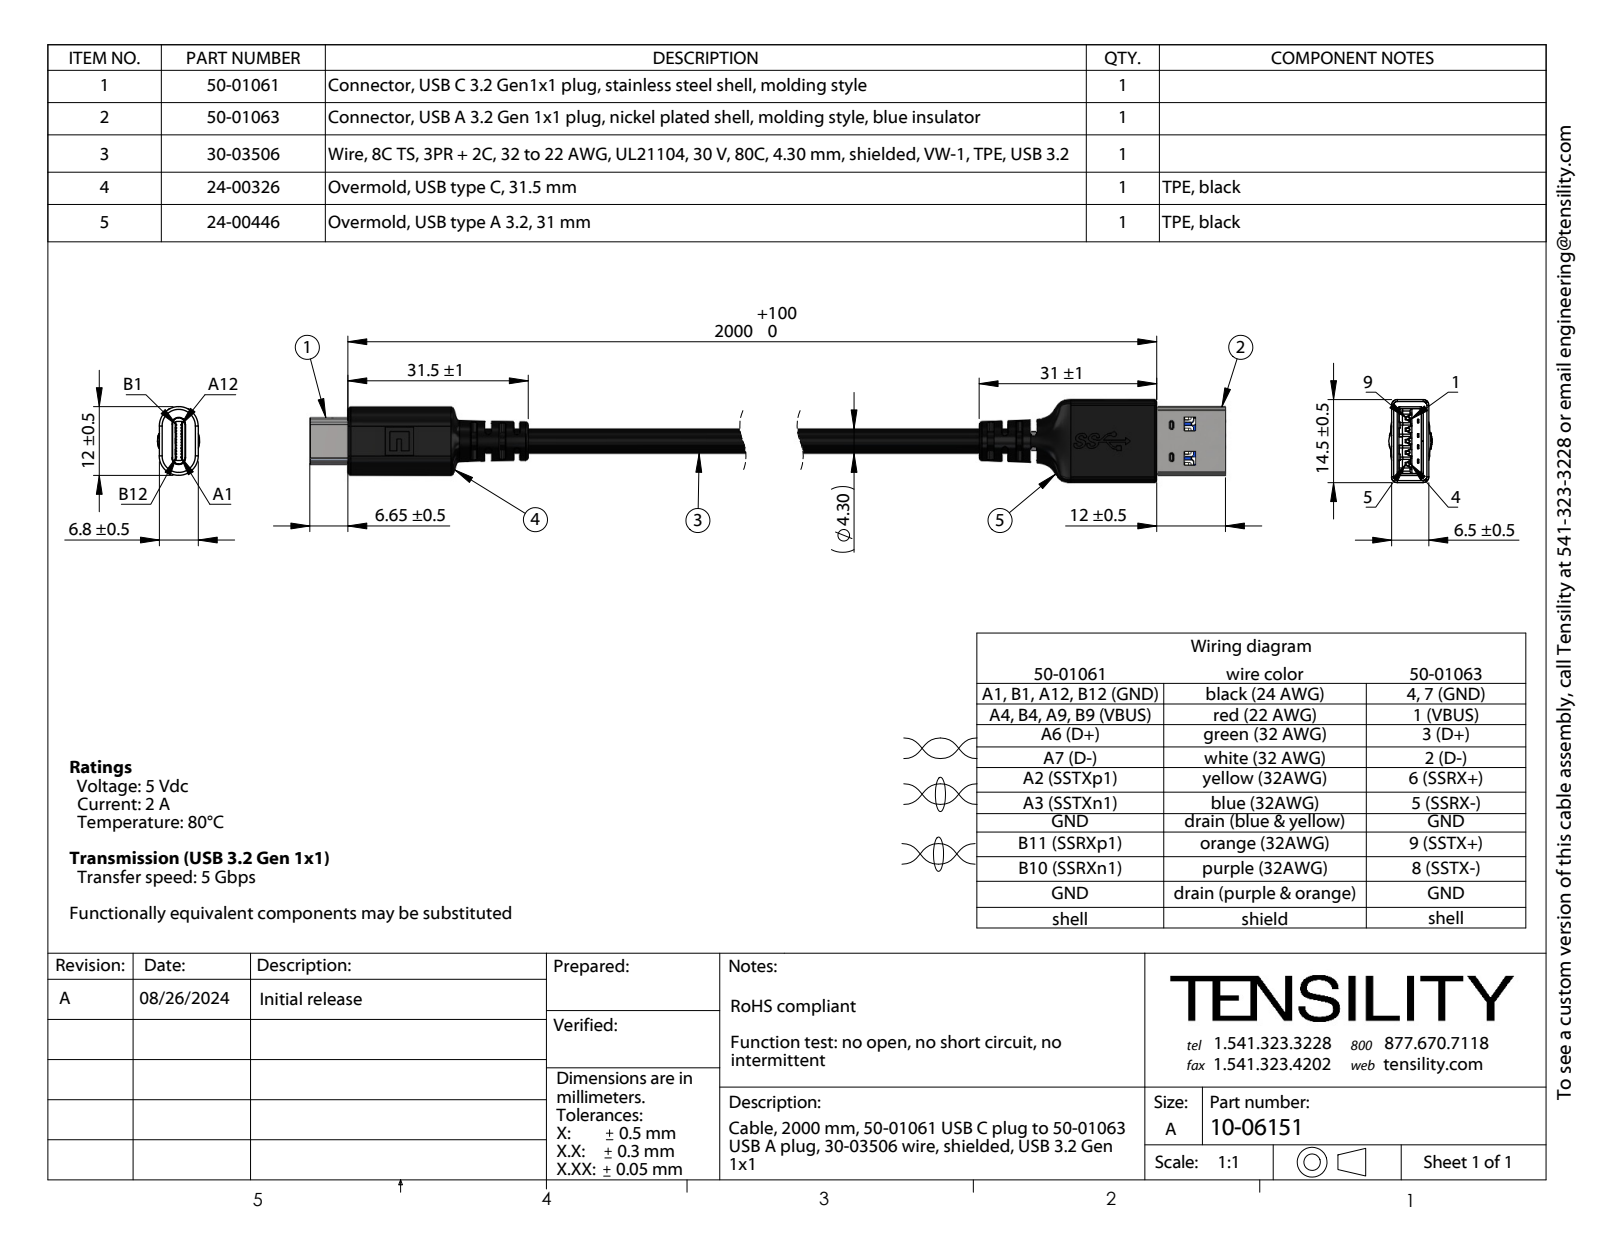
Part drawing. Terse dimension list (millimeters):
name: 50-01063_pin4; 30-03506_Spec; 50-01063_insulator; 50-01063_shell (+8 more)
written by: SolidWorks 2021 (CONFIG_CONTROL_DESIGN)
unit: mm
bodies: 184 solids, 2646 faces (1399 planar, 829 cylindrical, 418 other)
size: 211.15 × 14.5 × 7.54
volume: 5 792 mm³; area: 26 919 mm²
holes: 1× ⌀0.87, 1× ⌀3.23, 1× ⌀3.35
bosses: 4× ⌀0.6, 2× ⌀0.75, 2× ⌀0.55, 2× ⌀0.45, 1× ⌀4.3, 1× ⌀3.25, 1× ⌀1.66, 1× ⌀1
rounds: 30× R0.1, 24× R0.2, 20× R0.5, 13× R0.3, 10× R0.4, 9× R0.25, 7× R0.35, 7× R0.6
face distances: 0.89, 4.25, 0.9, 2.5, 0.35, 6.5, 0.88, 3.1, 1.28, 0.98
hole spacings: 0.33, 0.37, 0.32, 0.44, 1.67, 0.43, 1.56, 1.65
